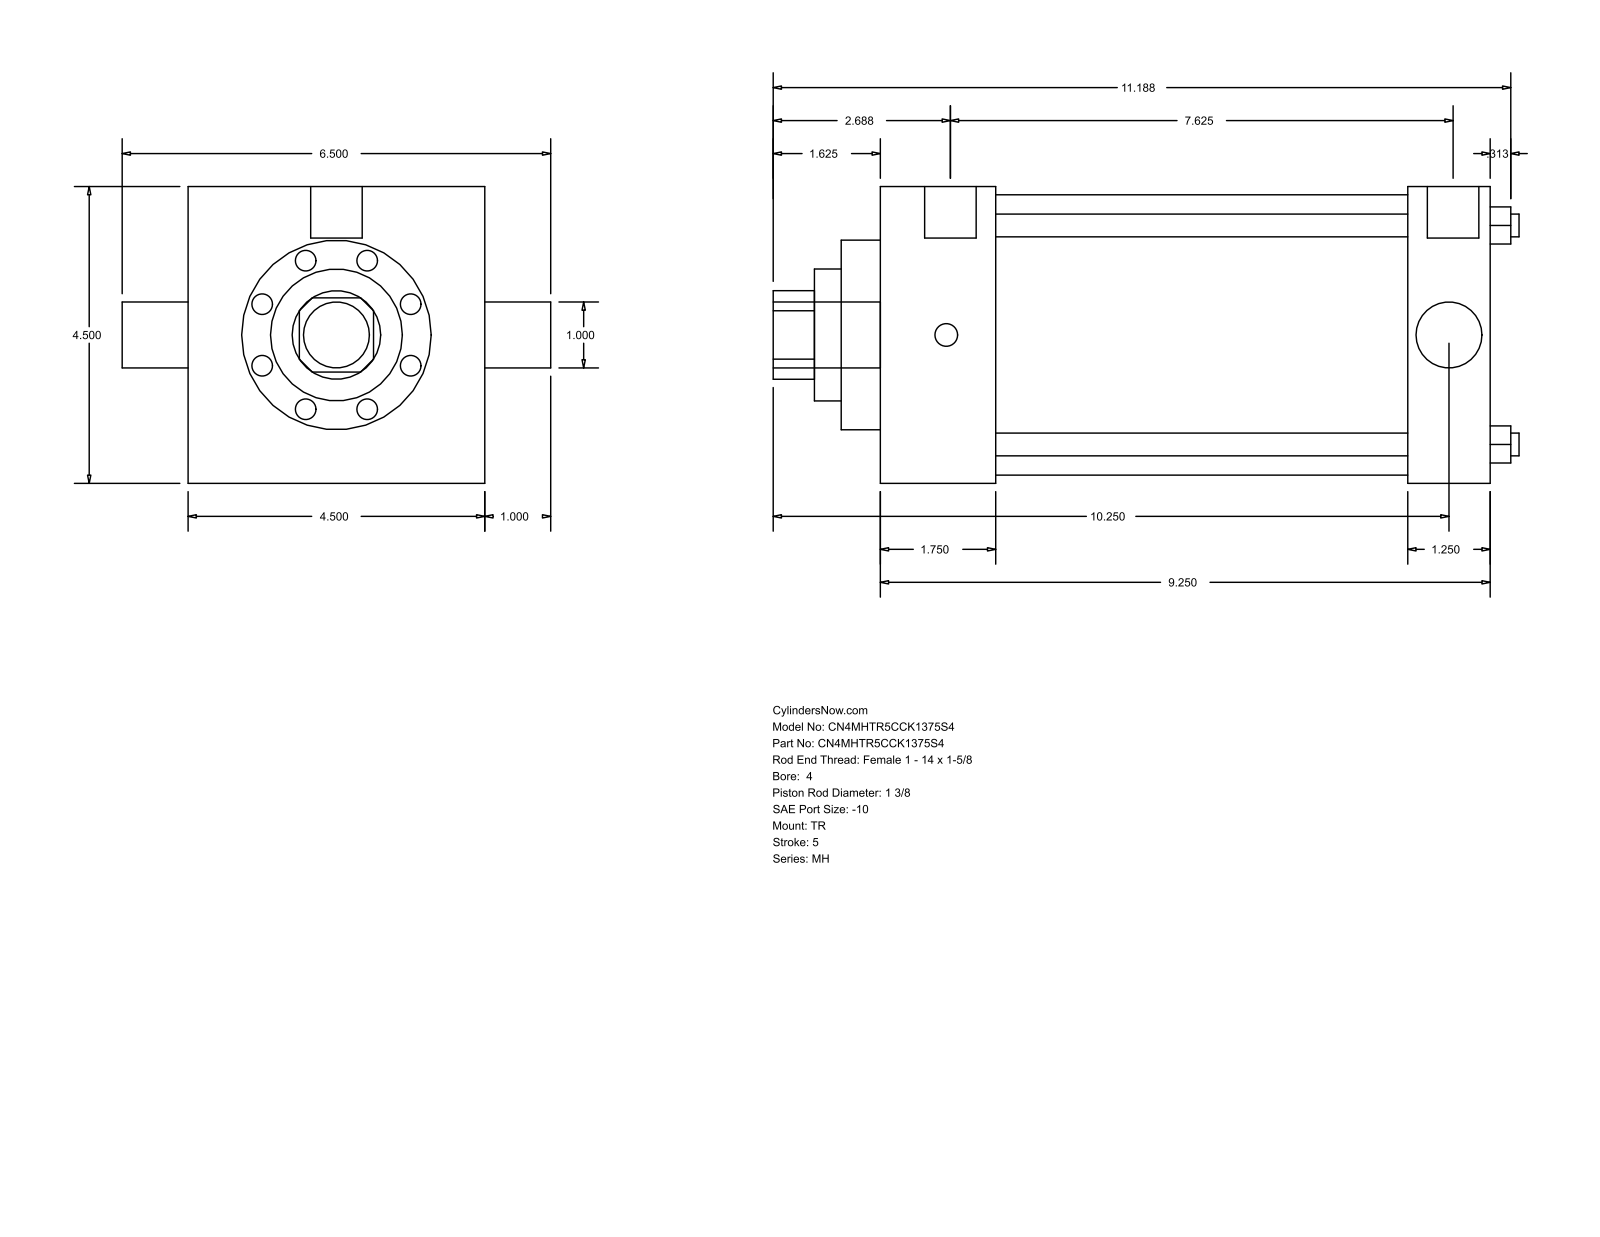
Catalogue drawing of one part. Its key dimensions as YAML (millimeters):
part_name: "MH_TR__0400_1.375"
step_written_by: "GSSL Pune (CONFIG_CONTROL_DESIGN)"
units: millimeters
bodies: {solids: 0, faces: 86, planar: 61, cylindrical: 25, other: 0}
overall_size: [287.34, 165.1, 114.3]
round_holes:
  - {diameter: 8.76, count: 4}
  - {diameter: 25.4, count: 1}
  - {diameter: 34.92, count: 1}
  - {diameter: 50.8, count: 1}
  - {diameter: 73.03, count: 1}
  - {diameter: 107.95, count: 1}
round_bosses_or_shafts:
  - {diameter: 8.73, count: 3}
  - {diameter: 19.84, count: 2}
  - {diameter: 25.4, count: 1}
partial_cylinders:
  - {radius: 17.06, count: 1}
face_to_face_distances: [114.3, 234.96, 44.45, 190.51, 203.2, 158.75, 31.76, 15.08, 59.53, 218.28]
hole_center_spacings: [59.62, 84.32, 119.25]
